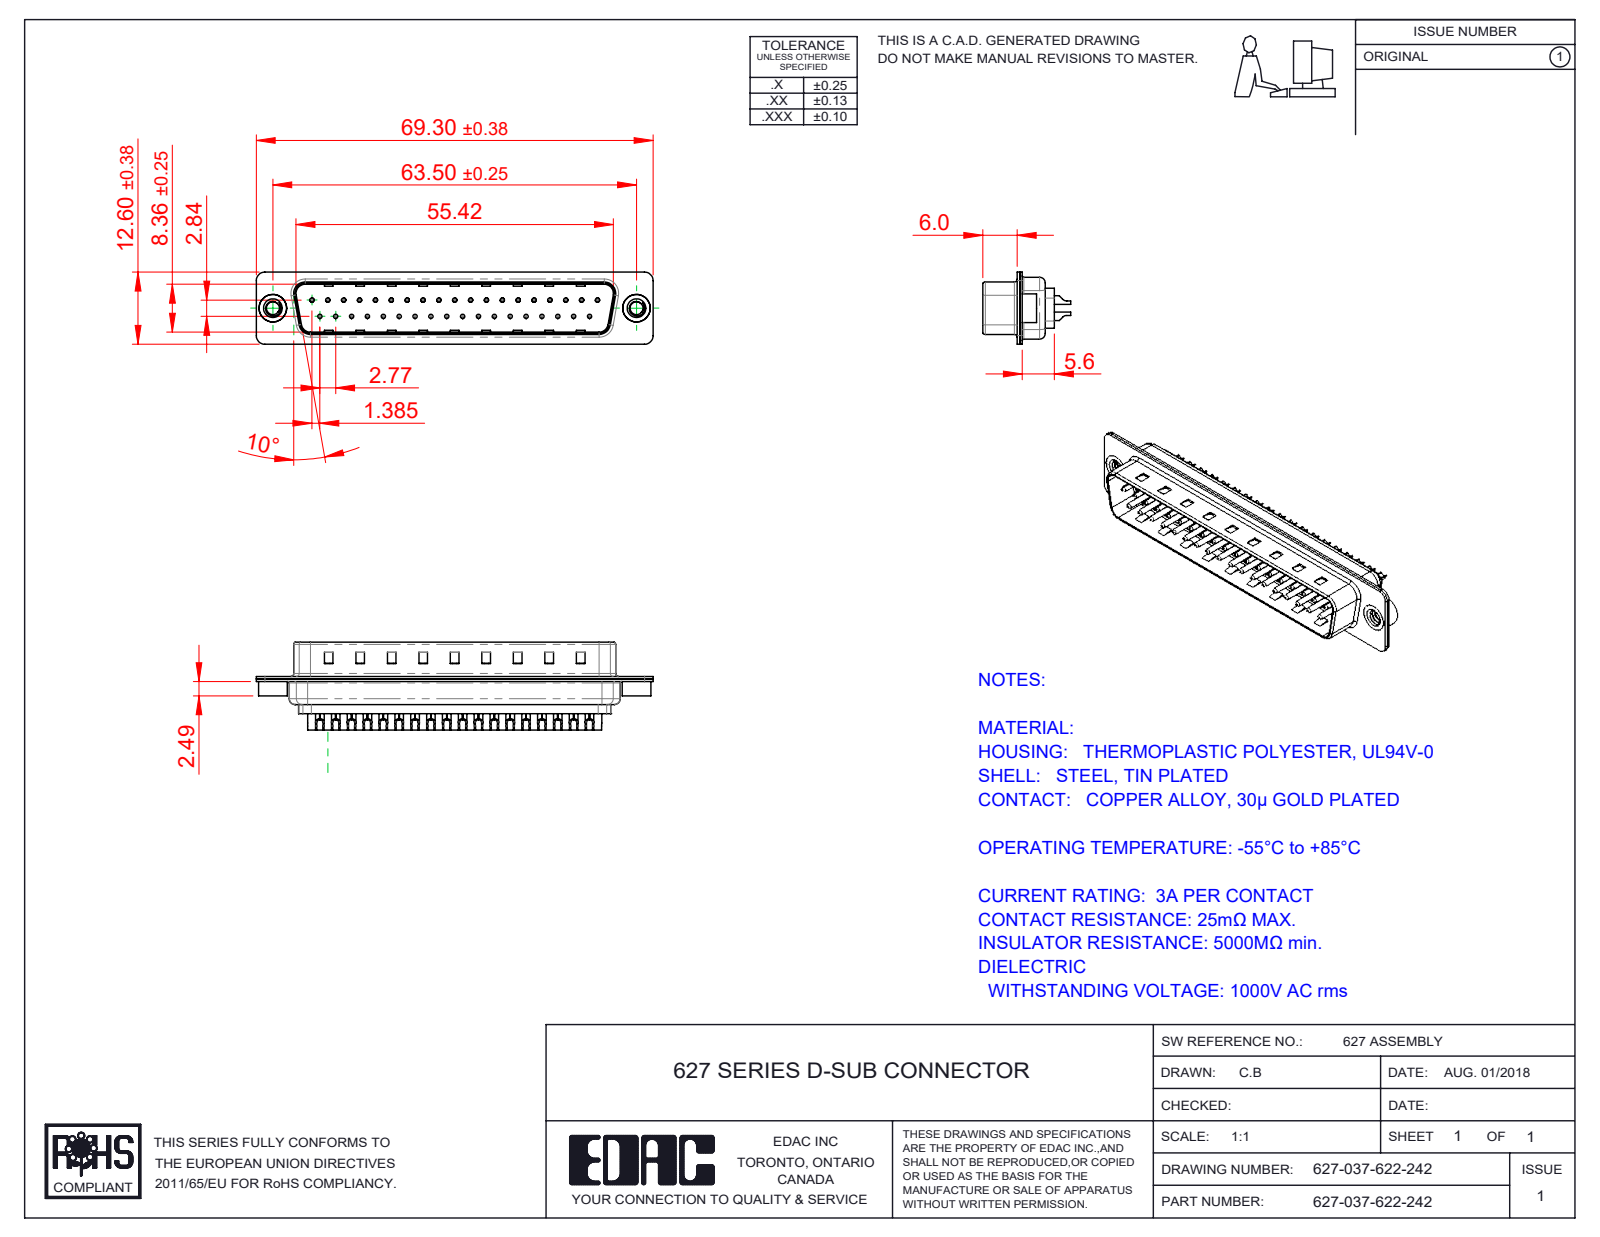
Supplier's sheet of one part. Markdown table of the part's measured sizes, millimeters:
| quantity | value |
| --- | --- |
| part name | 627 Shell Rear_37 Contacts; 627-037-622-042; 627 Contact Row 2_22L; 627 Housing_37 LP (+3 more) |
| STEP written by | SolidWorks 2020 (CONFIG_CONTROL_DESIGN) |
| units | millimeters |
| bodies | 42 solids, 2776 faces (721 planar, 1212 cylindrical, 843 other) |
| overall size | 69.3 × 15.35 × 12.6 |
| volume | 3 709 mm³ |
| surface area | 10 747 mm² |
| round holes (diameter × count) | 0.35 × 37, 1.1 × 37, 1.6 × 37, 2.26 × 2, 4 × 2, 4.8 × 2 |
| round bosses / shafts (diameter × count) | 2 × 37, 1.5 × 37, 0.75 × 37, 5 × 2, 4.9 × 2 |
| partial cylindrical surfaces (radius × count) | 1.5 × 16, 2 × 12, 0.5 × 8, 1.6 × 8, 1 × 6, 0.25 × 4, 0.6 × 4, 0.65 × 4 |
| main face-to-face distances | 0.4, 0.82, 9.58, 0.45, 8.76, 1.5, 0.9, 1.4, 6.05, 0.42 |
| hole center spacings | 3.16, 2.77, 5.54, 8.31, 5.04, 10.1, 11.08, 12.78 |
